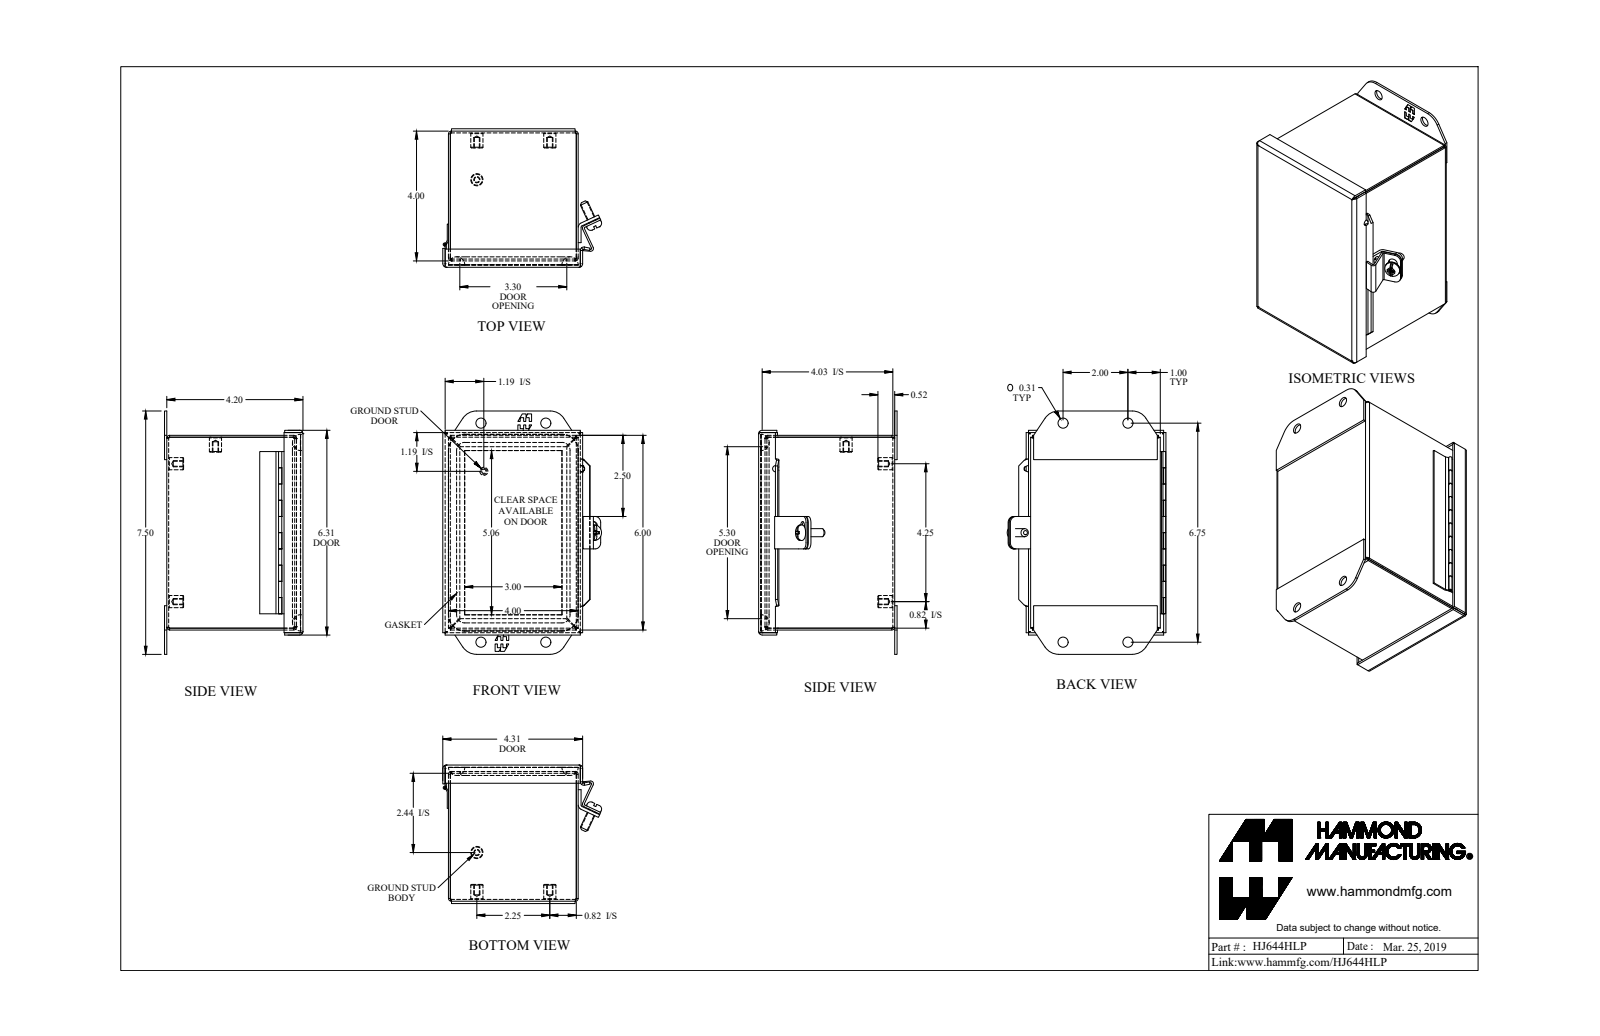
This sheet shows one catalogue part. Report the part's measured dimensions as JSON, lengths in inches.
{"part_name": "HJ644HLP", "step_written_by": "SolidWorks 2018 (AUTOMOTIVE_DESIGN)", "units": "inches", "bodies": {"solids": 17, "faces": 574, "planar": 307, "cylindrical": 165, "other": 102}, "overall_size": [7.5, 4.896, 4.269], "volume_in3": 11.93, "surface_area_in2": 382.1, "round_holes": [[0.156, 5], [0.313, 4], [0.05, 1], [0.213, 1]], "round_bosses_or_shafts": [[0.375, 5], [0.25, 2], [0.48, 1], [0.188, 1], [0.1, 1], [0.045, 1]], "partial_cylinders_radius": [[0.188, 14], [0.029, 10], [0.086, 10], [0.036, 5], [0.108, 5], [0.25, 4], [0.499, 4], [0.5, 4]], "face_to_face_distances": [0.057, 3.943, 0.072, 4.197, 4.125, 5.943, 4, 3.886, 0.057, 4.068], "hole_center_spacings": [1.257, 5.502, 2.465, 5.896, 2, 4.25, 6.75, 7.041]}
